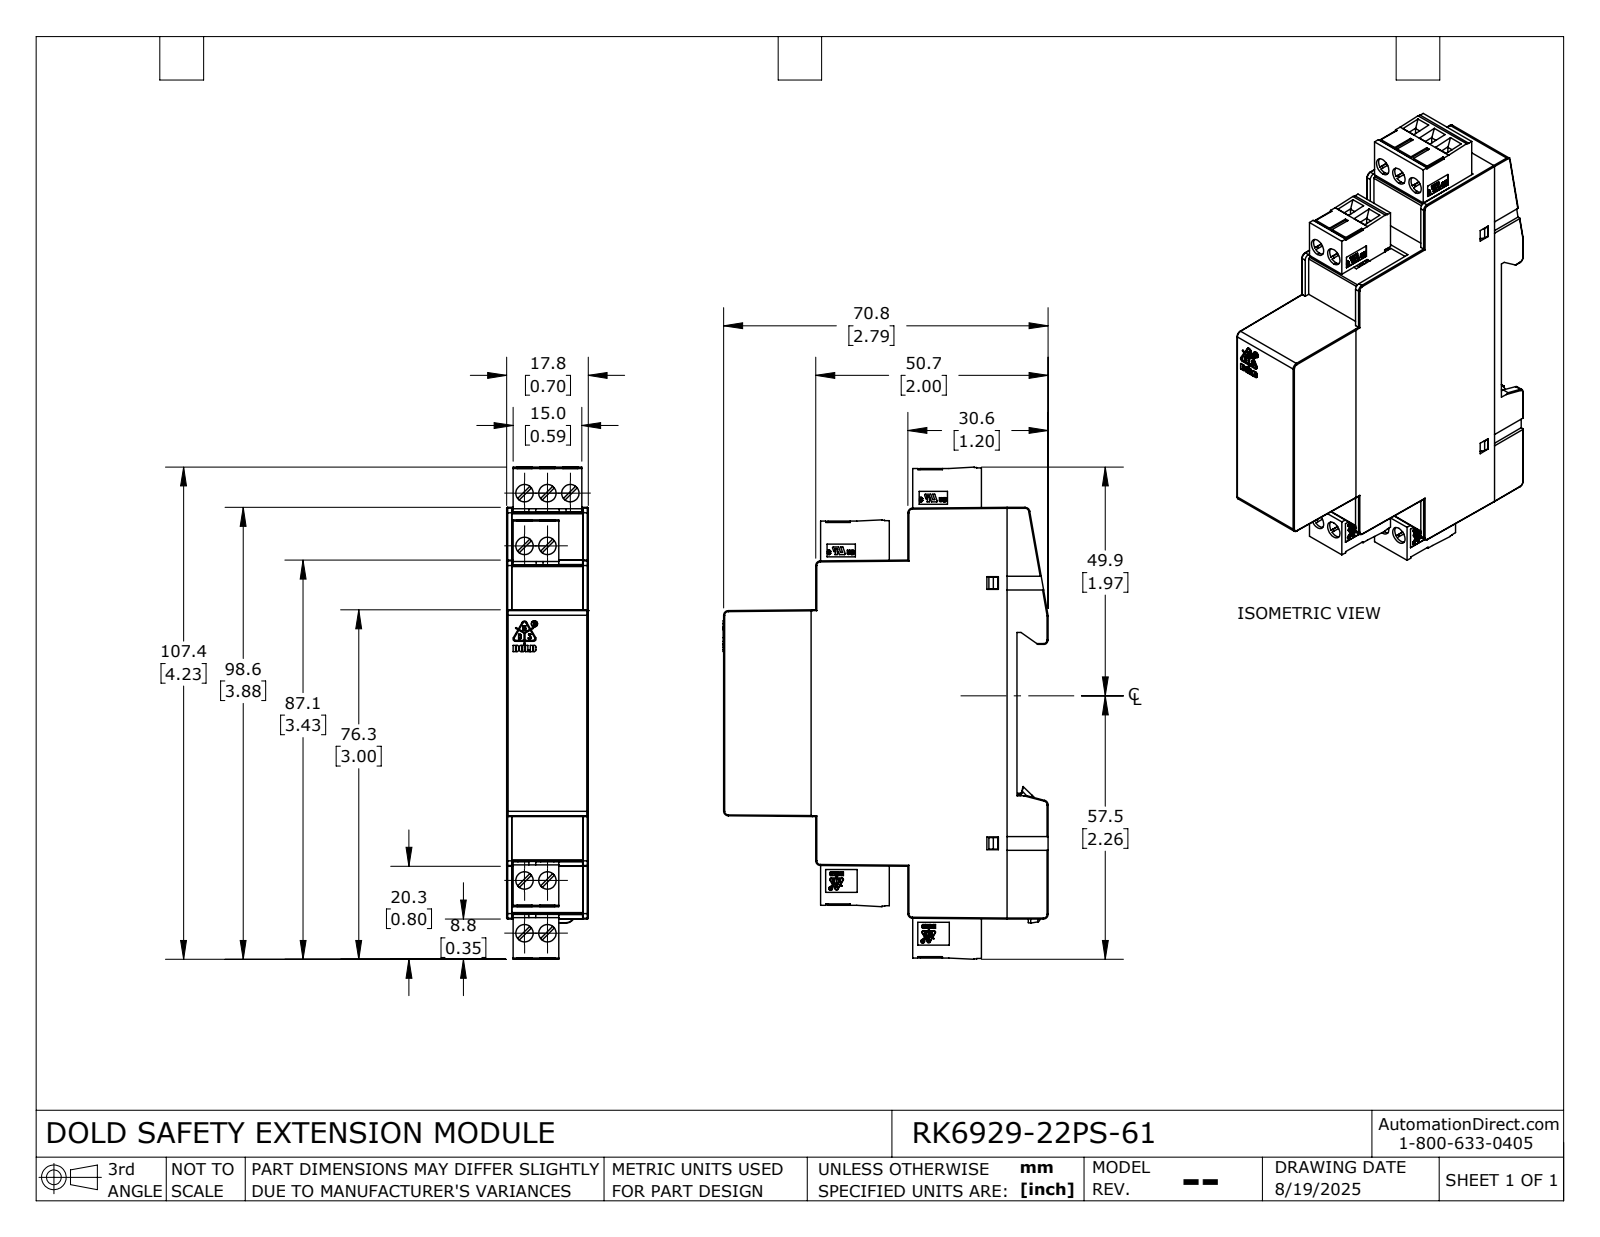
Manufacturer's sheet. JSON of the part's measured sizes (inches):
{"part_name": "RK6929-22PS-61", "step_written_by": "SolidWorks 2024 (AUTOMOTIVE_DESIGN)", "units": "inches", "bodies": {"solids": 1, "faces": 2365, "planar": 1802, "cylindrical": 485, "other": 78}, "overall_size": [4.228, 2.791, 0.701], "volume_in3": 5.169, "surface_area_in2": 36.74, "round_holes": [[0.15, 8], [0.03, 4], [0.138, 4], [0.05, 1]], "round_bosses_or_shafts": [[0.032, 4], [0.054, 1]], "partial_cylinders_radius": [[0.008, 42], [0.01, 40], [0.02, 23], [0.039, 13], [0.004, 9], [0.012, 9], [0.005, 8], [0.007, 8]], "face_to_face_distances": [0.701, 0.791, 2.52, 0.646, 0.449, 0.252, 0.055, 0.394, 0.453, 0.36], "hole_center_spacings": [0.197, 0.453, 0.494, 3.327, 3.333, 0.791, 0.815, 0.912]}
